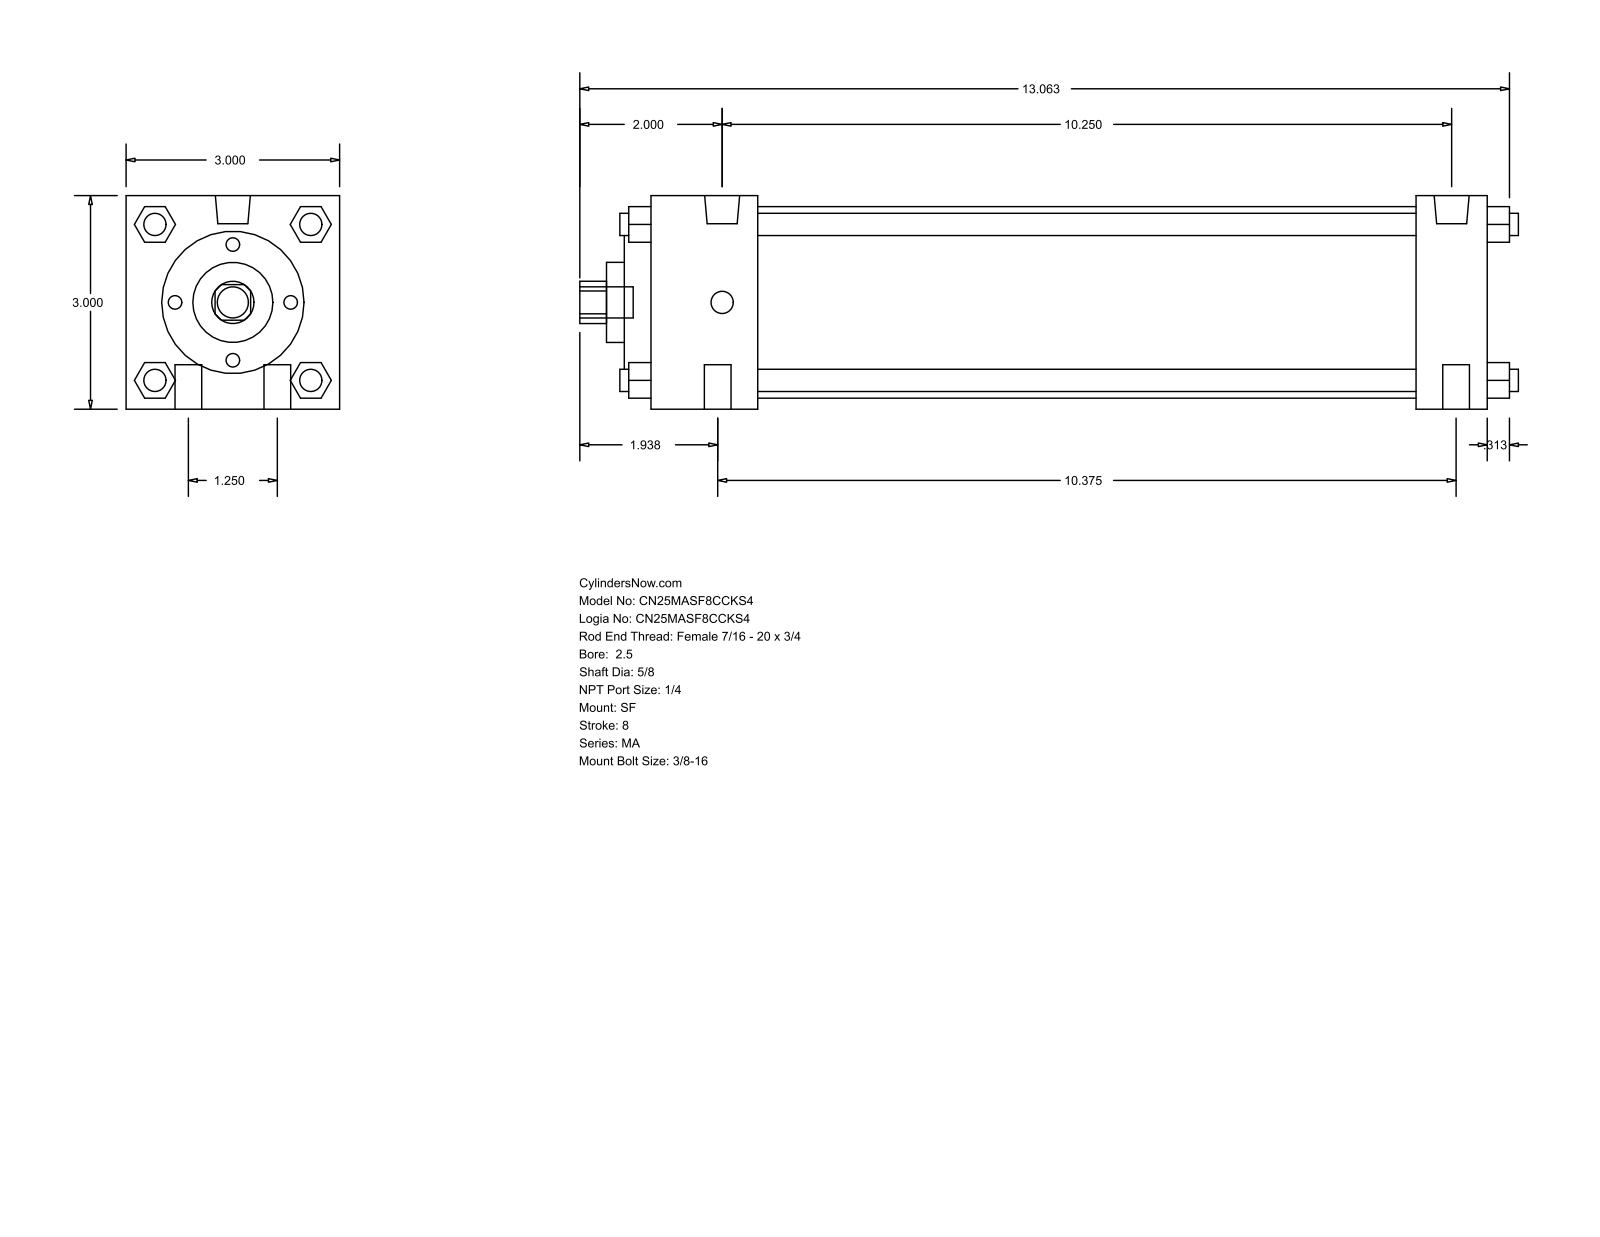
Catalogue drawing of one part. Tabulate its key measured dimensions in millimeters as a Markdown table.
| quantity | value |
| --- | --- |
| part name | MA_SF__0250_0.625 |
| STEP written by | GSSL Pune (CONFIG_CONTROL_DESIGN) |
| units | millimeters |
| bodies | 0 solids, 126 faces (95 planar, 31 cylindrical, 0 other) |
| overall size | 334.96 × 76.2 × 76.2 |
| round holes (diameter × count) | 15.88 × 1, 28.57 × 1, 50.8 × 1, 68.33 × 1 |
| round bosses / shafts (diameter × count) | 7.94 × 6, 9.53 × 4, 12.49 × 2, 11.11 × 1 |
| partial cylindrical surfaces (radius × count) | 7.54 × 1 |
| main face-to-face distances | 76.2, 298.45, 25.4, 273.05, 38.1, 234.95, 260.35, 12.7, 9.52, 47.62 |
